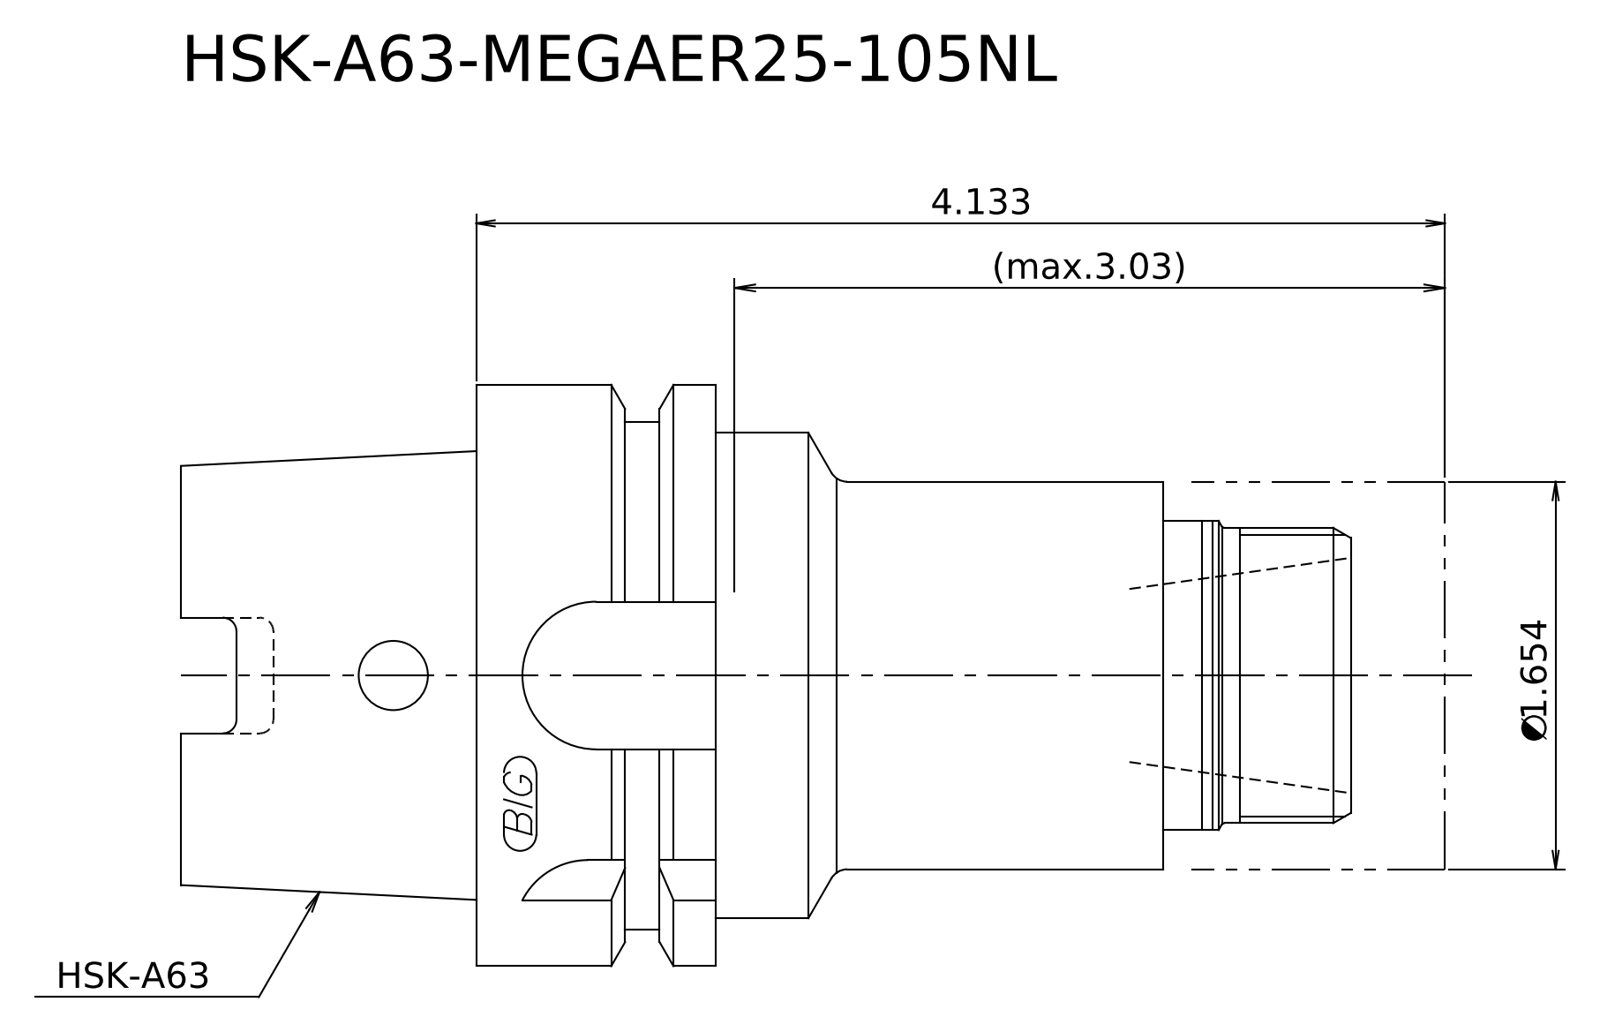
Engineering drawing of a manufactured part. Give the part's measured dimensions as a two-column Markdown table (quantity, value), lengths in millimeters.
| quantity | value |
| --- | --- |
| STEP written by | Kubotek KeyCreator 2011 V10.0.2 (22737) (automotive_design) |
| units | millimeters |
| bodies | 2 solids, 23 faces (9 planar, 8 cylindrical, 6 other) |
| overall size | 137 × 63 × 63 |
| volume | 264 602 mm³ |
| surface area | 31 562 mm² |
| round bosses / shafts (diameter × count) | 63 × 1, 55 × 1, 52.6 × 1, 42 × 1, 33.5 × 1, 32 × 1 |
| main face-to-face distances | 109.5, 27.5, 137, 105, 77.5, 32, 79, 51.5, 26, 58 |
